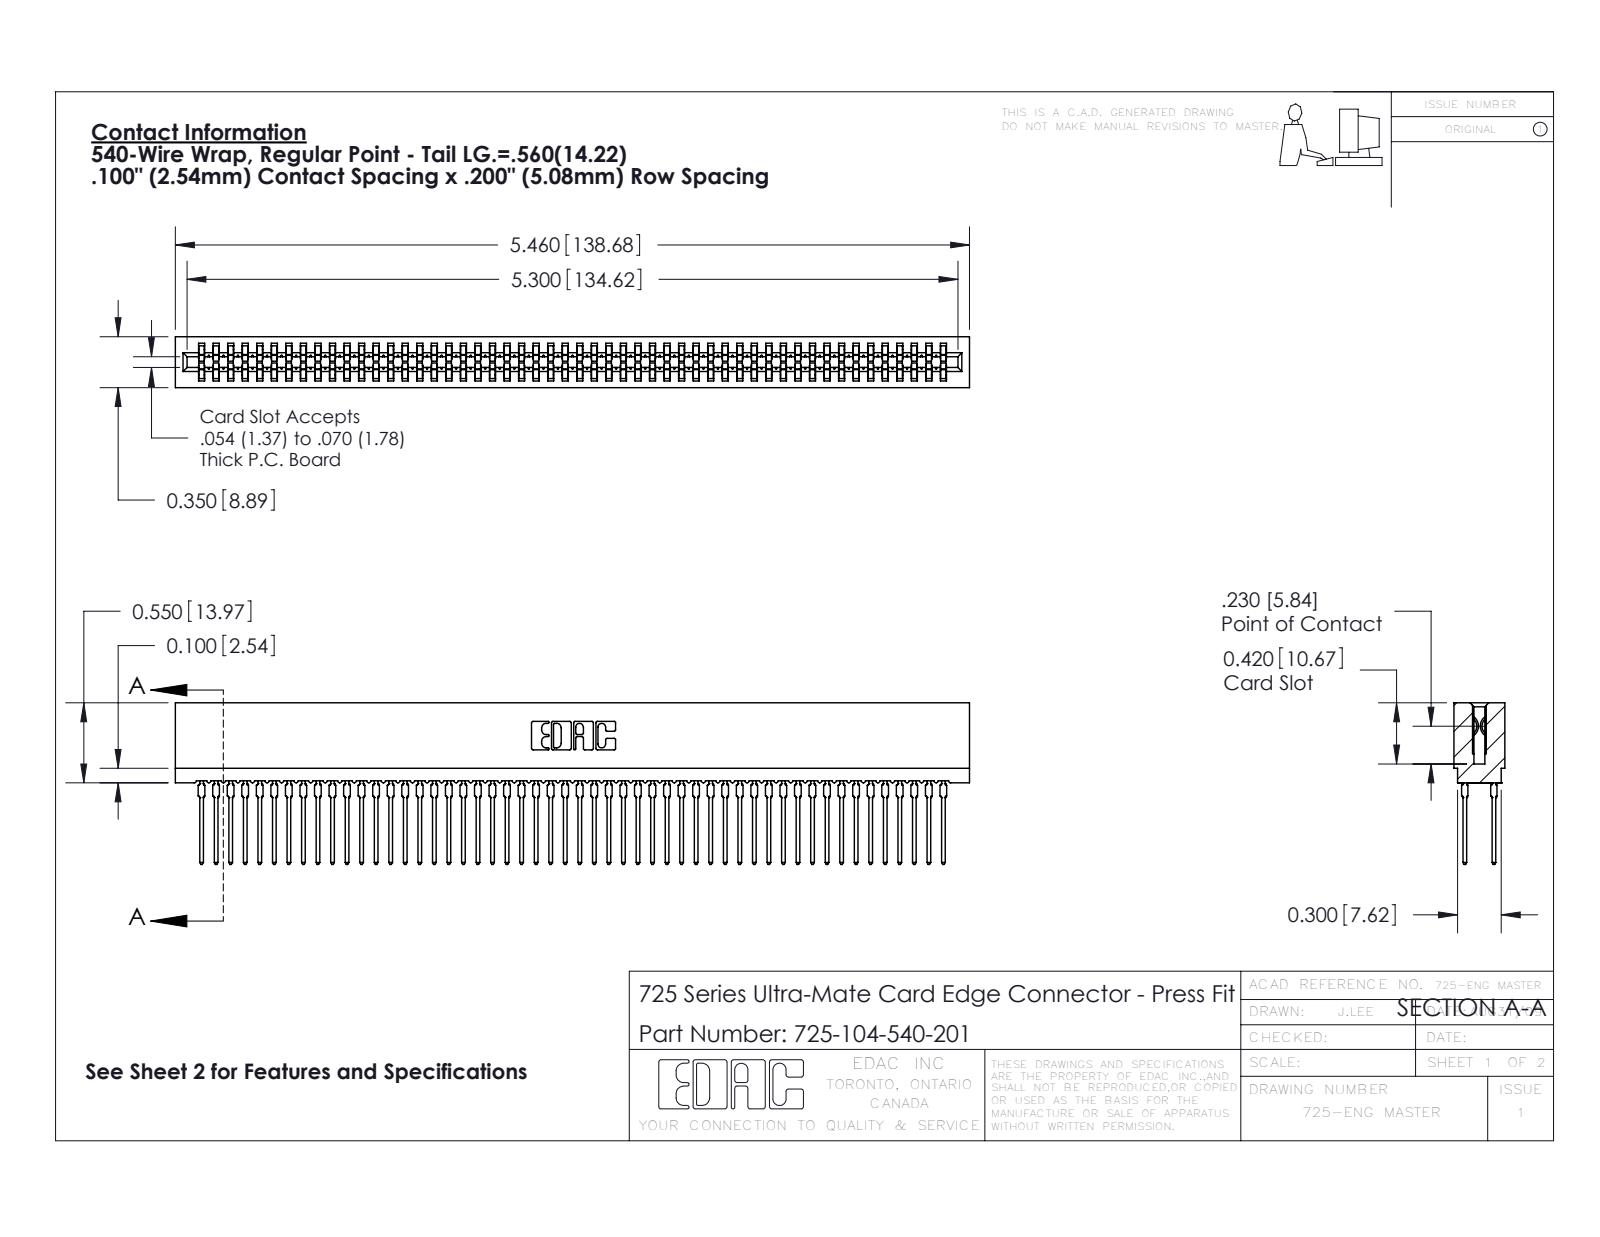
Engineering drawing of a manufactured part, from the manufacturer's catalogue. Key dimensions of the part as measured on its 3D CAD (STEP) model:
Part name (STEP PRODUCT): 745-292-001_540; 725-104-540-201; 725 Part_Insulator Option - 01
STEP written by: SolidWorks 2016 (CONFIG_CONTROL_DESIGN)
Units: inches
Bodies: 105 solids, 9403 faces (4839 planar, 1860 cylindrical, 2704 other)
Overall size (bounding box): 5.46 × 1.11 × 0.35
Volume: 0.687 in³ · Surface area: 39.04 in²
Partial cylindrical surfaces — rounded edges, fillets, slot ends (radius × count): R0.021 ×208, R0.015 ×104, R0.01 ×22, R0.005 ×8, R0.011 ×8, R0.007 ×6, R0.031 ×6, R0.026 ×3
Main face-to-face distances: 0.2, 0.063, 0.287, 0.35, 0.212, 0.138, 0.076, 0.149, 0.087, 0.263
